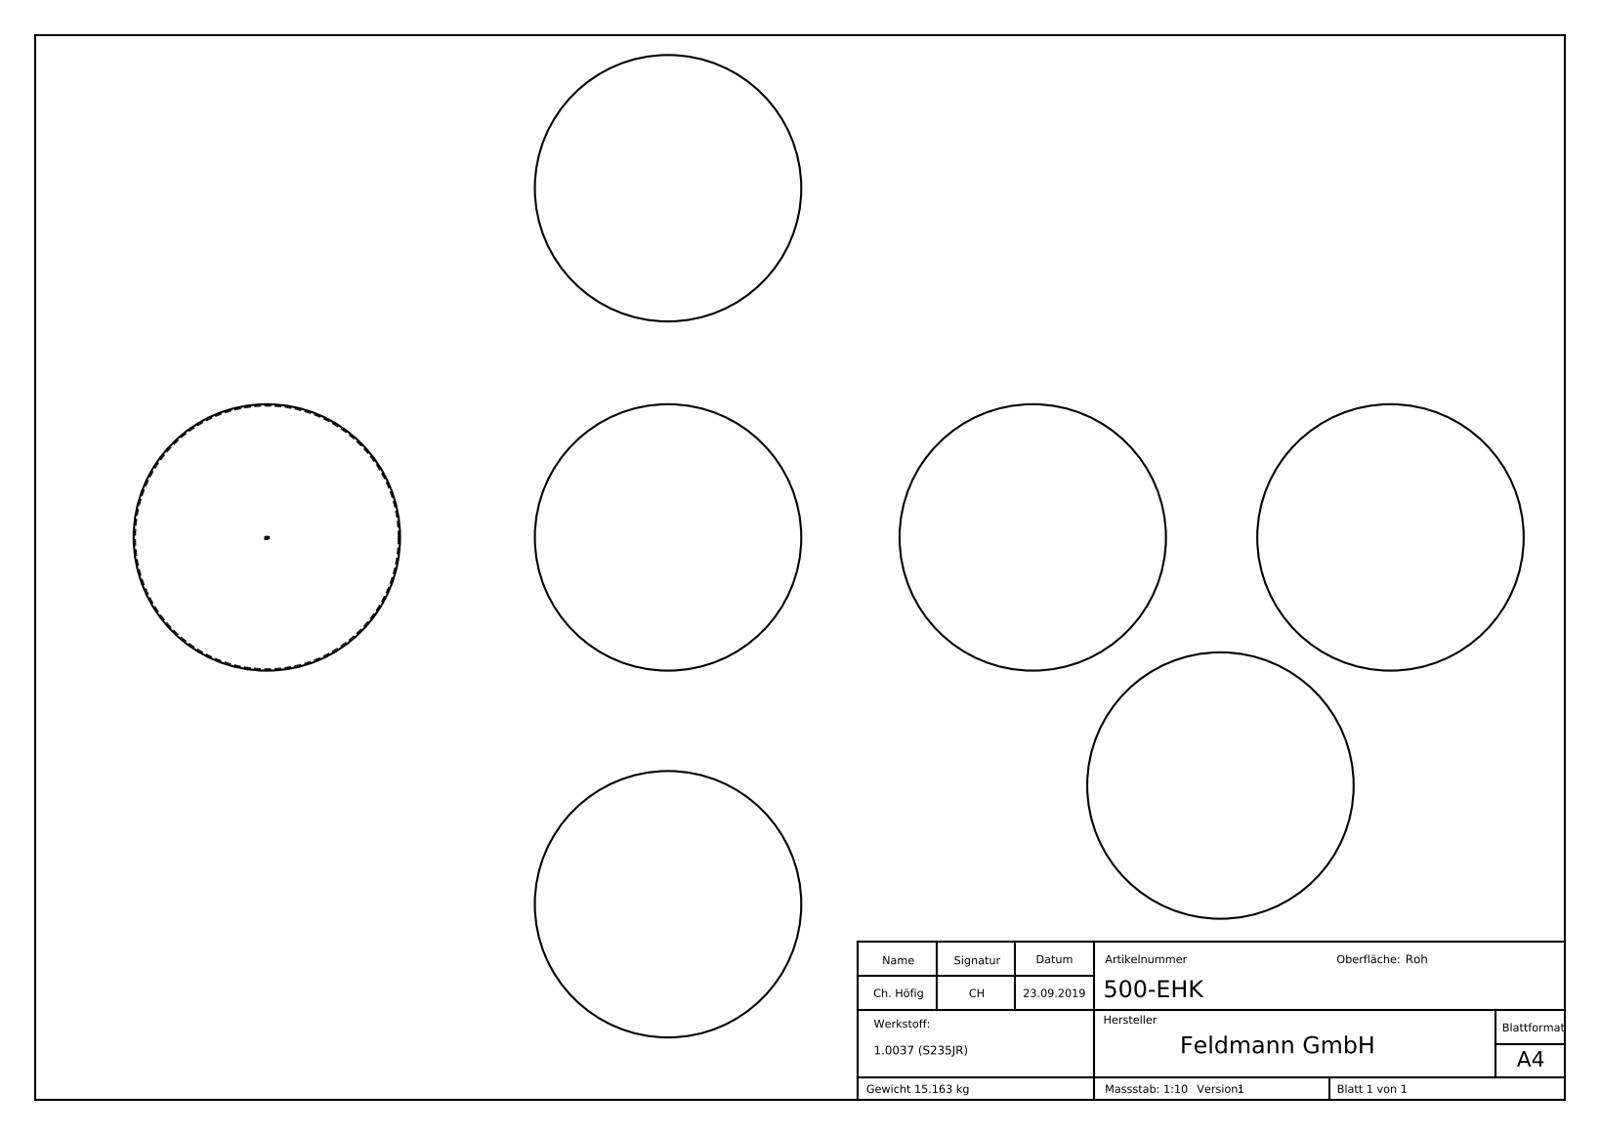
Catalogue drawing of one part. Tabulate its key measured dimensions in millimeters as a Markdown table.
| quantity | value |
| --- | --- |
| part name | 500-EHK |
| STEP written by | SolidWorks 2015 (CONFIG_CONTROL_DESIGN) |
| units | millimeters |
| bodies | 1 solid, 199 faces (99 planar, 0 cylindrical, 100 other) |
| overall size | 500 × 500 × 500 |
| volume | 1 944 000 mm³ |
| surface area | 1 555 000 mm² |
| main face-to-face distances | 3.2, 1.26, 4.5, 0.46, 3.59, 3.13, 0.68, 0.54, 0.64, 3.47 |
